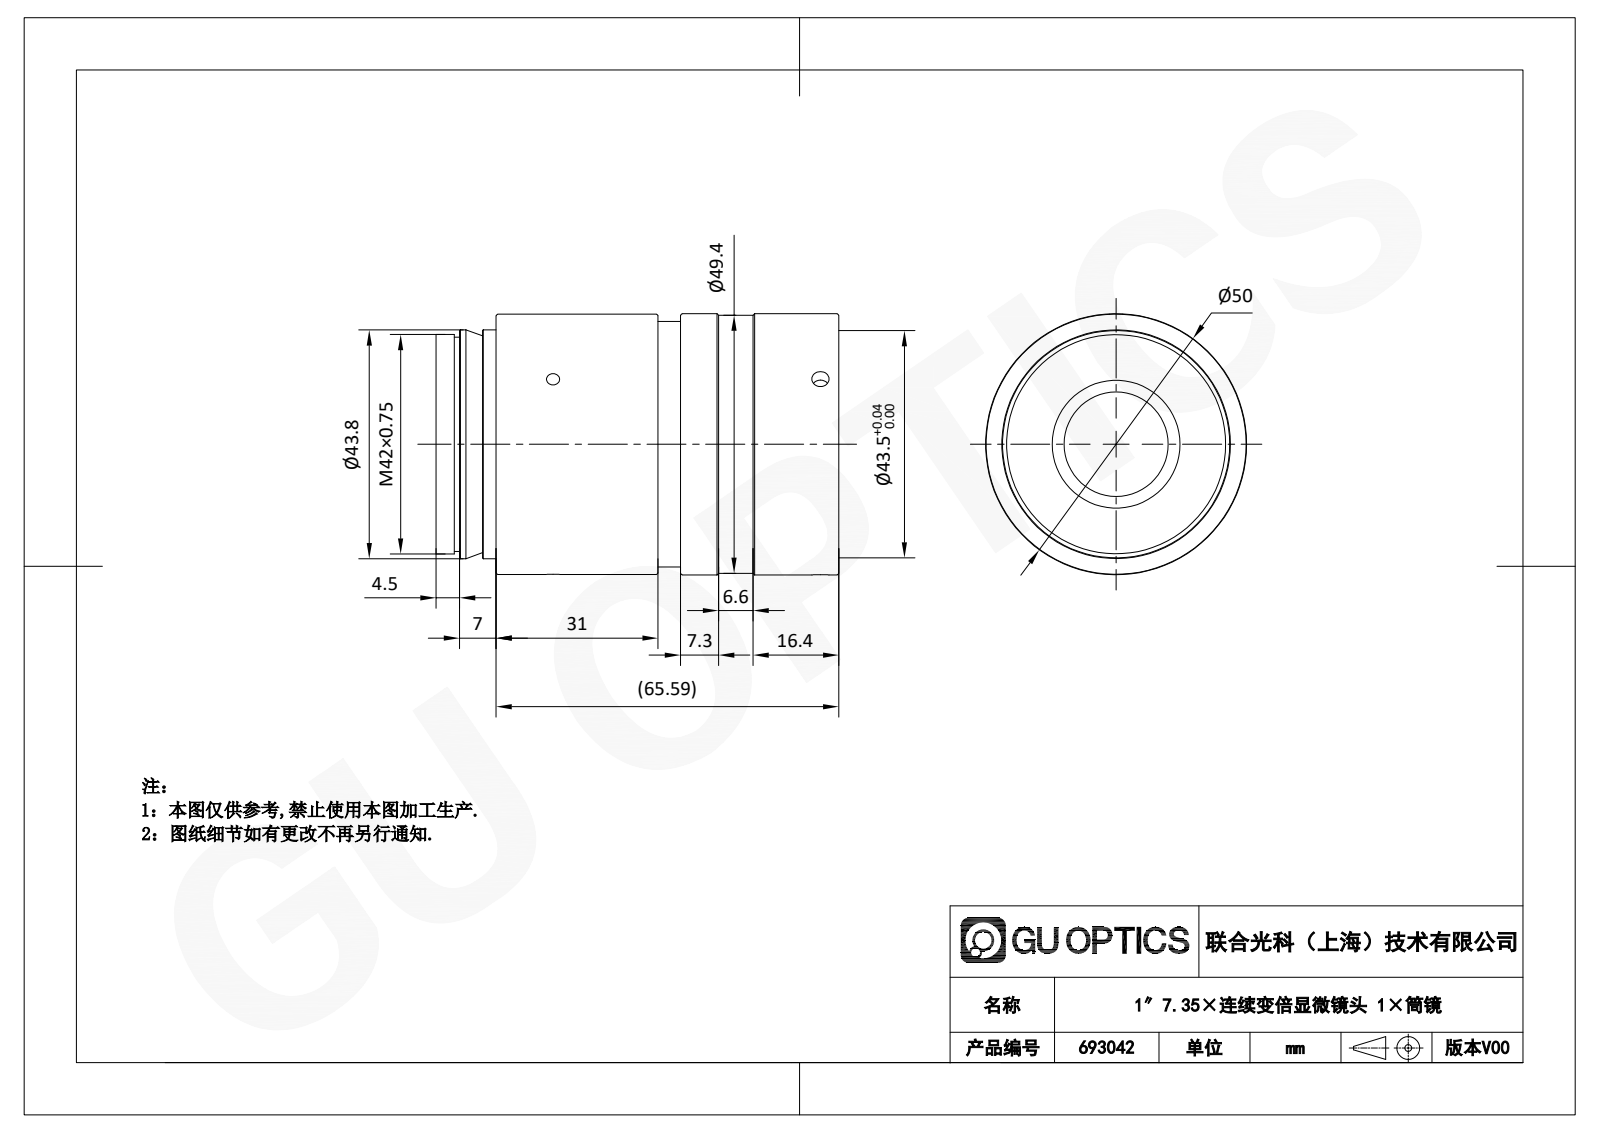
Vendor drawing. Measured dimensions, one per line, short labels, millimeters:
name: 693042
written by: SolidWorks 2020 (CONFIG_CONTROL_DESIGN)
unit: mm
bodies: 0 solids, 130 faces (43 planar, 20 cylindrical, 67 other)
size: 77.09 × 50 × 50
holes: 3× ⌀2.5, 3× ⌀3.3, 1× ⌀24.5, 1× ⌀32, 1× ⌀43.5
bosses: 1× ⌀50, 1× ⌀49.8, 1× ⌀49.4, 1× ⌀47, 1× ⌀43.8, 1× ⌀42, 1× ⌀41, 1× ⌀20
face distances: 66.3, 54.8, 11.5, 10.8, 65.6, 77.1, 68.8, 58, 3.2, 8.3
hole spacings: 51.2
